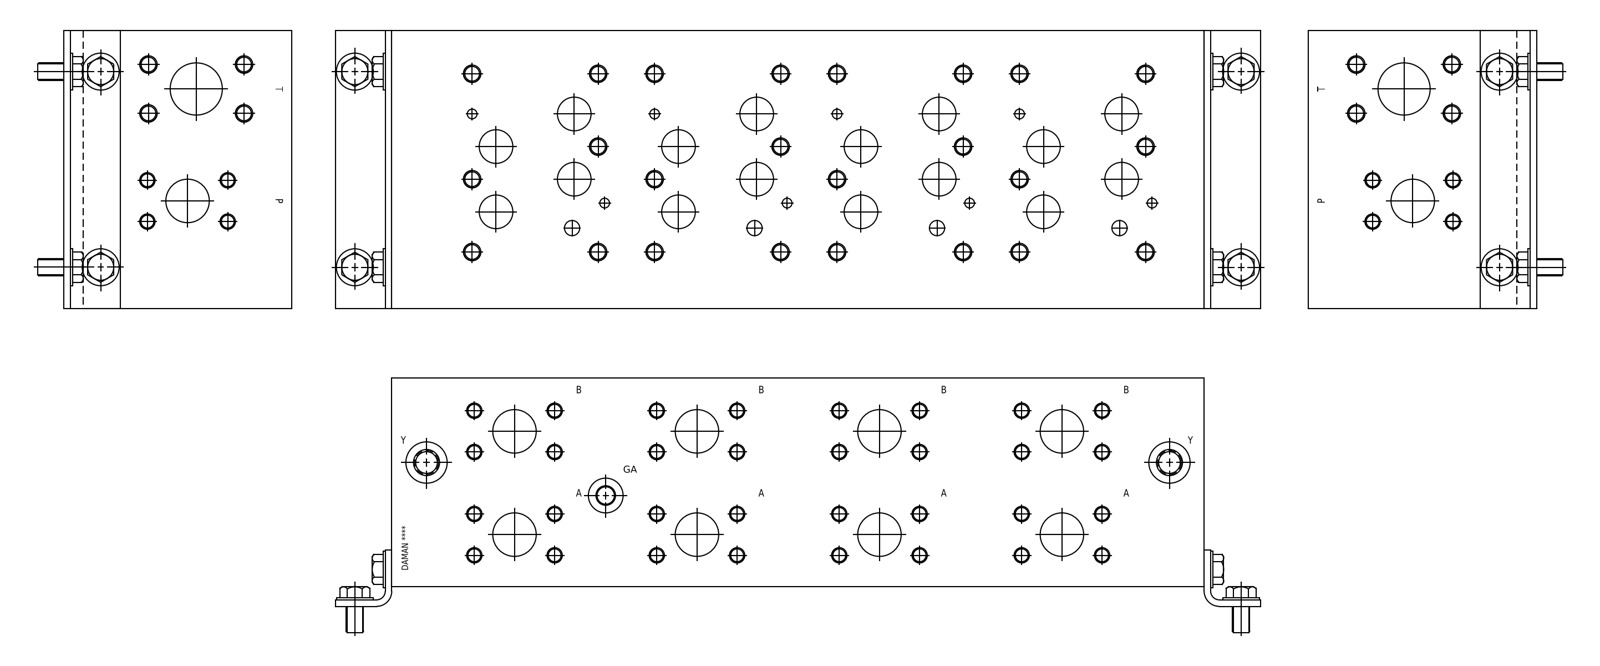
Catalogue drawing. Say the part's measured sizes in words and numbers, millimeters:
The part is named "Part_DD08HP045F_3D". Its 3-D file was written by "Autodesk Inventor 2020 (AUTOMOTIVE_DESIGN)". It is 1 solid with 1001 faces: 500 planar, 207 cylindrical and 294 other. Overall it measures 593.73 by 203.2 by 152.4 millimeters. Its volume is 17 890 000 cubic millimeters and its surface area 606 664 square millimeters. Round holes: 43 of diameter 11.13, 39 of diameter 9.35, 32 of diameter 12.7, 30 of diameter 10.72, 16 of diameter 24.61, 9 of diameter 31.75, 8 of diameter 7.14, 2 of diameter 17.5, 2 of diameter 19.05, 2 of diameter 19.25, 2 of diameter 30.63, 1 of diameter 12.29. The main face-to-face distances are 152.4, 203.2, 593.73, 30.23, 28.45, 0.79, 202.41, 27.66, 174.75, 122.17. The hole center spacings are 133.35, 266.7, 30.18, 153.2, 58.72, 66.02, 136.72, 75.41.
